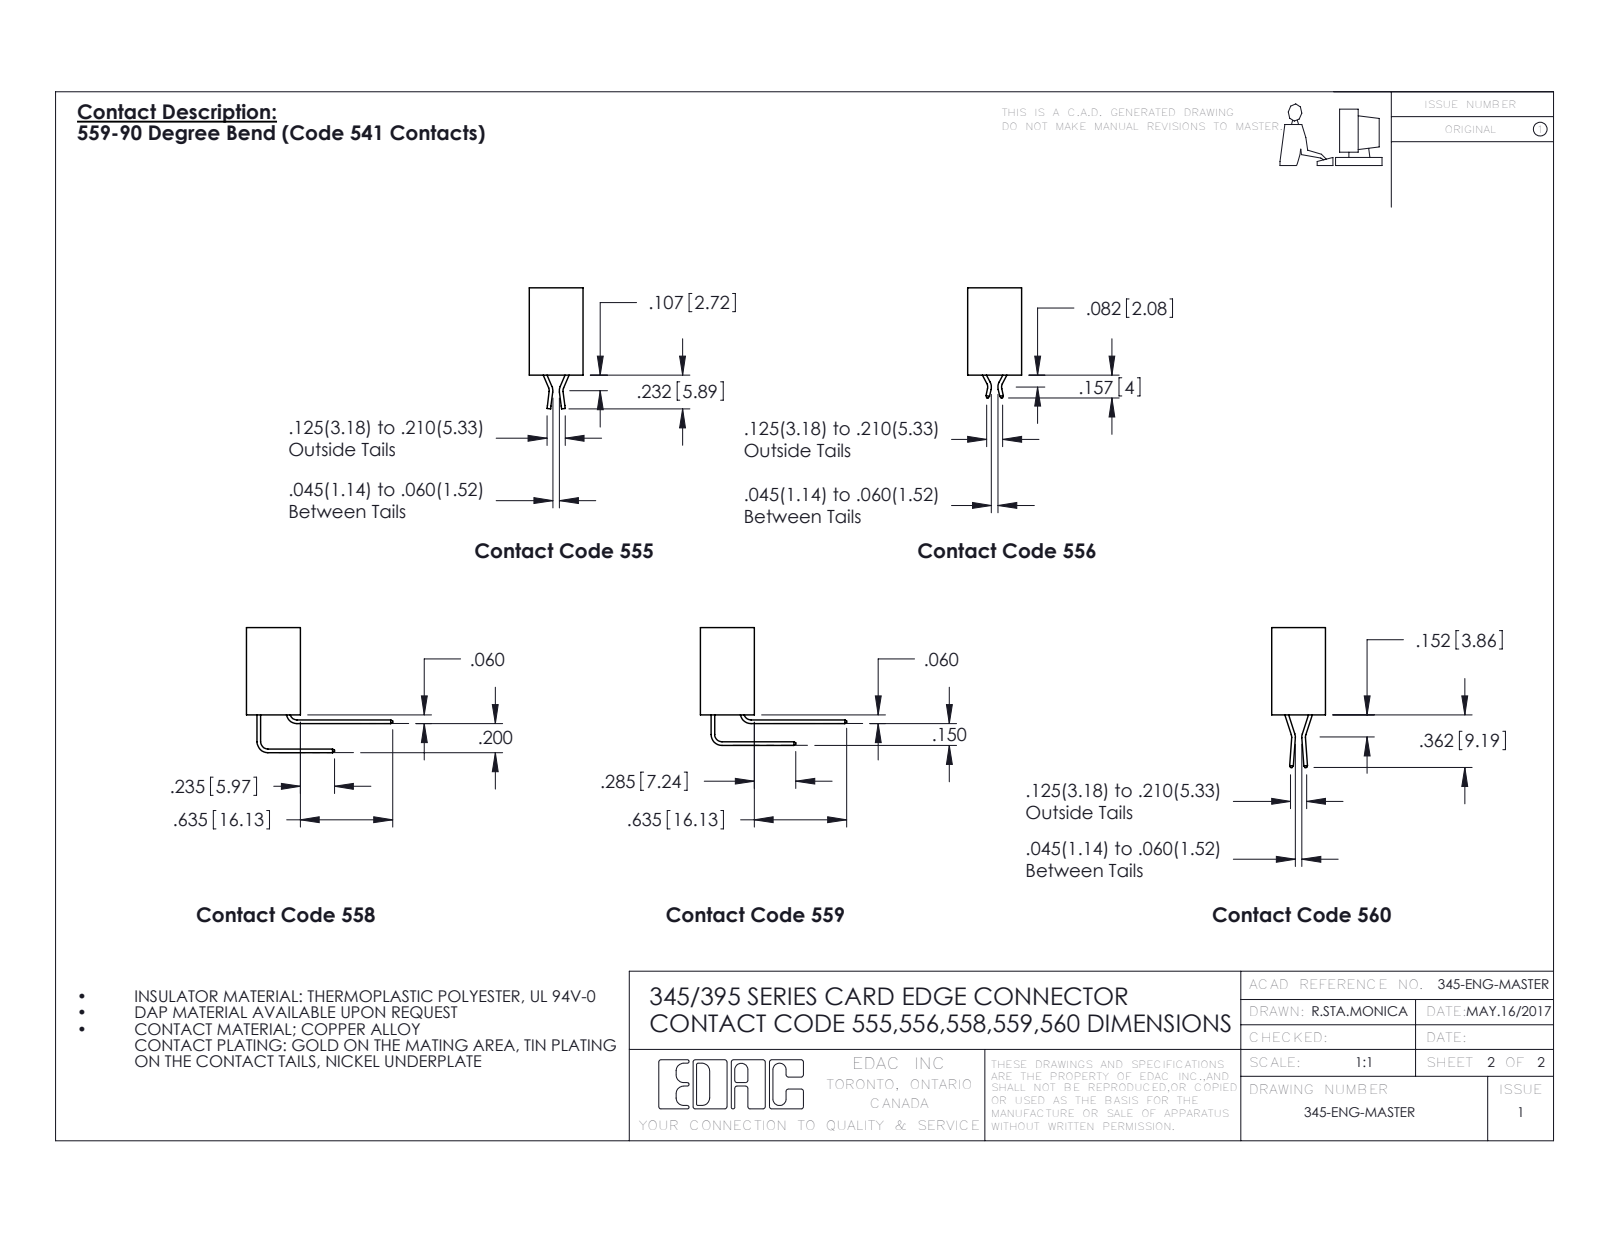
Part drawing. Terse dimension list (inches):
name: 395-047-559-101; 345-292-001_558 559 Tail - 1; 345 Part_No Mounting Lugs
written by: SolidWorks 2016 (CONFIG_CONTROL_DESIGN)
unit: in
bodies: 48 solids, 2938 faces (2050 planar, 888 cylindrical, 0 other)
size: 4.96 × 1.005 × 0.659
volume: 0.778 in³; area: 28.08 in²
holes: 1× ⌀0.064
rounds: 94× R0.006, 22× R0.01, 6× R0.007, 6× R0.031, 3× R0.026, 2× R0.031, 2× R0.04, 1× R0.014
face distances: 0.298, 0.072, 0.37, 0.2, 0.098, 0.272, 0.025, 0.225, 0.149, 0.072
